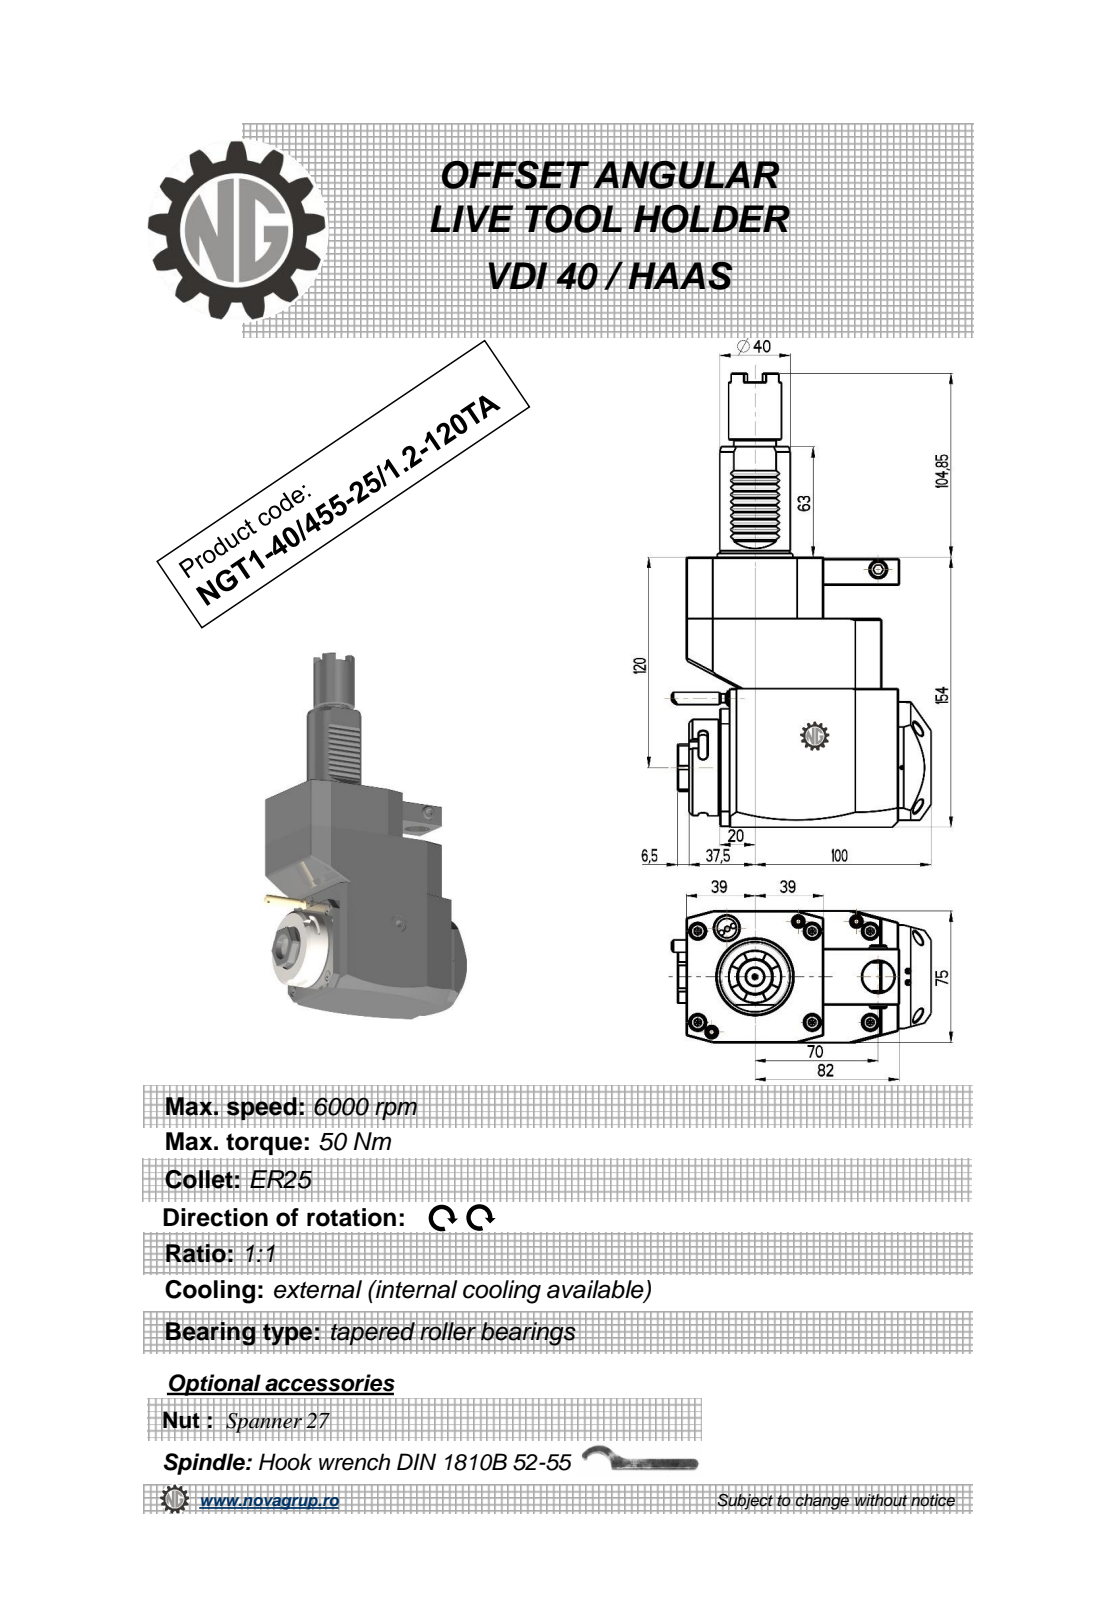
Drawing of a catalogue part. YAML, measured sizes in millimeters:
part_name: "NGT1_40_455_25_1_2_120TA"
step_written_by: "PRO/ENGINEER BY PARAMETRIC TECHNOLOGY CORPORATION, 2010280 (CONFIG_CONTROL_DESIGN)"
units: millimeters
bodies: {solids: 1, faces: 374, planar: 216, cylindrical: 76, other: 82}
overall_size: [258.85, 147.33, 75]
volume: 1299000
surface_area: 94272
round_holes:
  - {diameter: 18, count: 2}
  - {diameter: 2.5, count: 1}
  - {diameter: 3, count: 1}
  - {diameter: 9.5, count: 1}
round_bosses_or_shafts:
  - {diameter: 8.96, count: 2}
  - {diameter: 55, count: 1}
  - {diameter: 48, count: 1}
  - {diameter: 40, count: 1}
  - {diameter: 30, count: 1}
  - {diameter: 20, count: 1}
  - {diameter: 10, count: 1}
  - {diameter: 7, count: 1}
partial_cylinders:
  - {radius: 0.3, count: 10}
  - {radius: 2.5, count: 6}
  - {radius: 180, count: 2}
  - {radius: 0.5, count: 1}
  - {radius: 4.25, count: 1}
  - {radius: 15, count: 1}
  - {radius: 24.5, count: 1}
  - {radius: 37.5, count: 1}
face_to_face_distances: [75, 154, 19, 119, 59, 111, 92, 35, 17.5, 53.5]
hole_center_spacings: [43.2, 75.07, 112.5]
